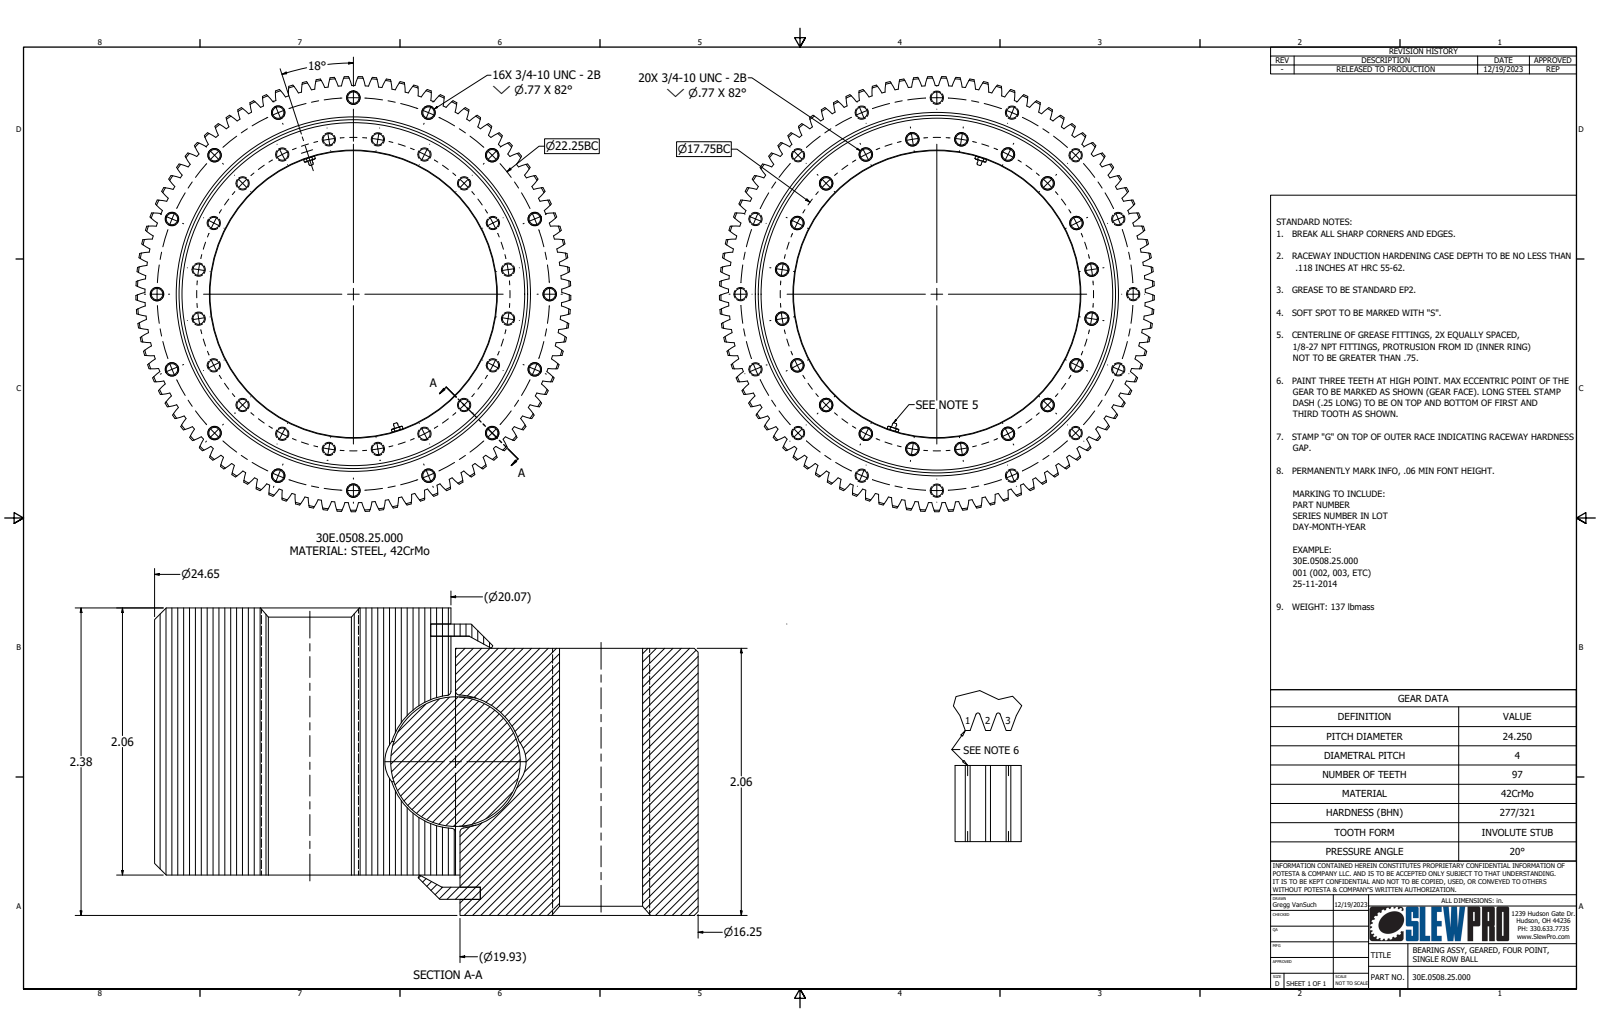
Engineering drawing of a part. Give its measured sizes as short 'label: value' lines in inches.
name: 30E.0508.25.000; Spur Gears1; HGF_11
written by: Autodesk Inventor 2026 (AUTOMOTIVE_DESIGN)
unit: in
bodies: 7 solids, 877 faces (36 planar, 444 cylindrical, 397 other)
size: 24.649 × 24.647 × 2.375
volume: 483.5 in³; area: 1 738 in²
holes: 36× ⌀0.642, 2× ⌀0.063, 2× ⌀0.109, 1× ⌀1.126, 1× ⌀16.25, 1× ⌀19.617, 1× ⌀20, 1× ⌀20.07, 1× ⌀20.383
bosses: 1× ⌀20.383, 1× ⌀19.93, 1× ⌀19.617, 1× ⌀1.125
rounds: 194× R3.495, 1× R11.812, 1× R12.325
face distances: 2.063, 0.312, 1.751, 2.375, 0.094, 1.939, 2.032, 0.094, 0.124, 2.25
hole spacings: 4.341, 12.361, 18.5, 2.777, 8.515, 8.515, 8.875, 11.125
